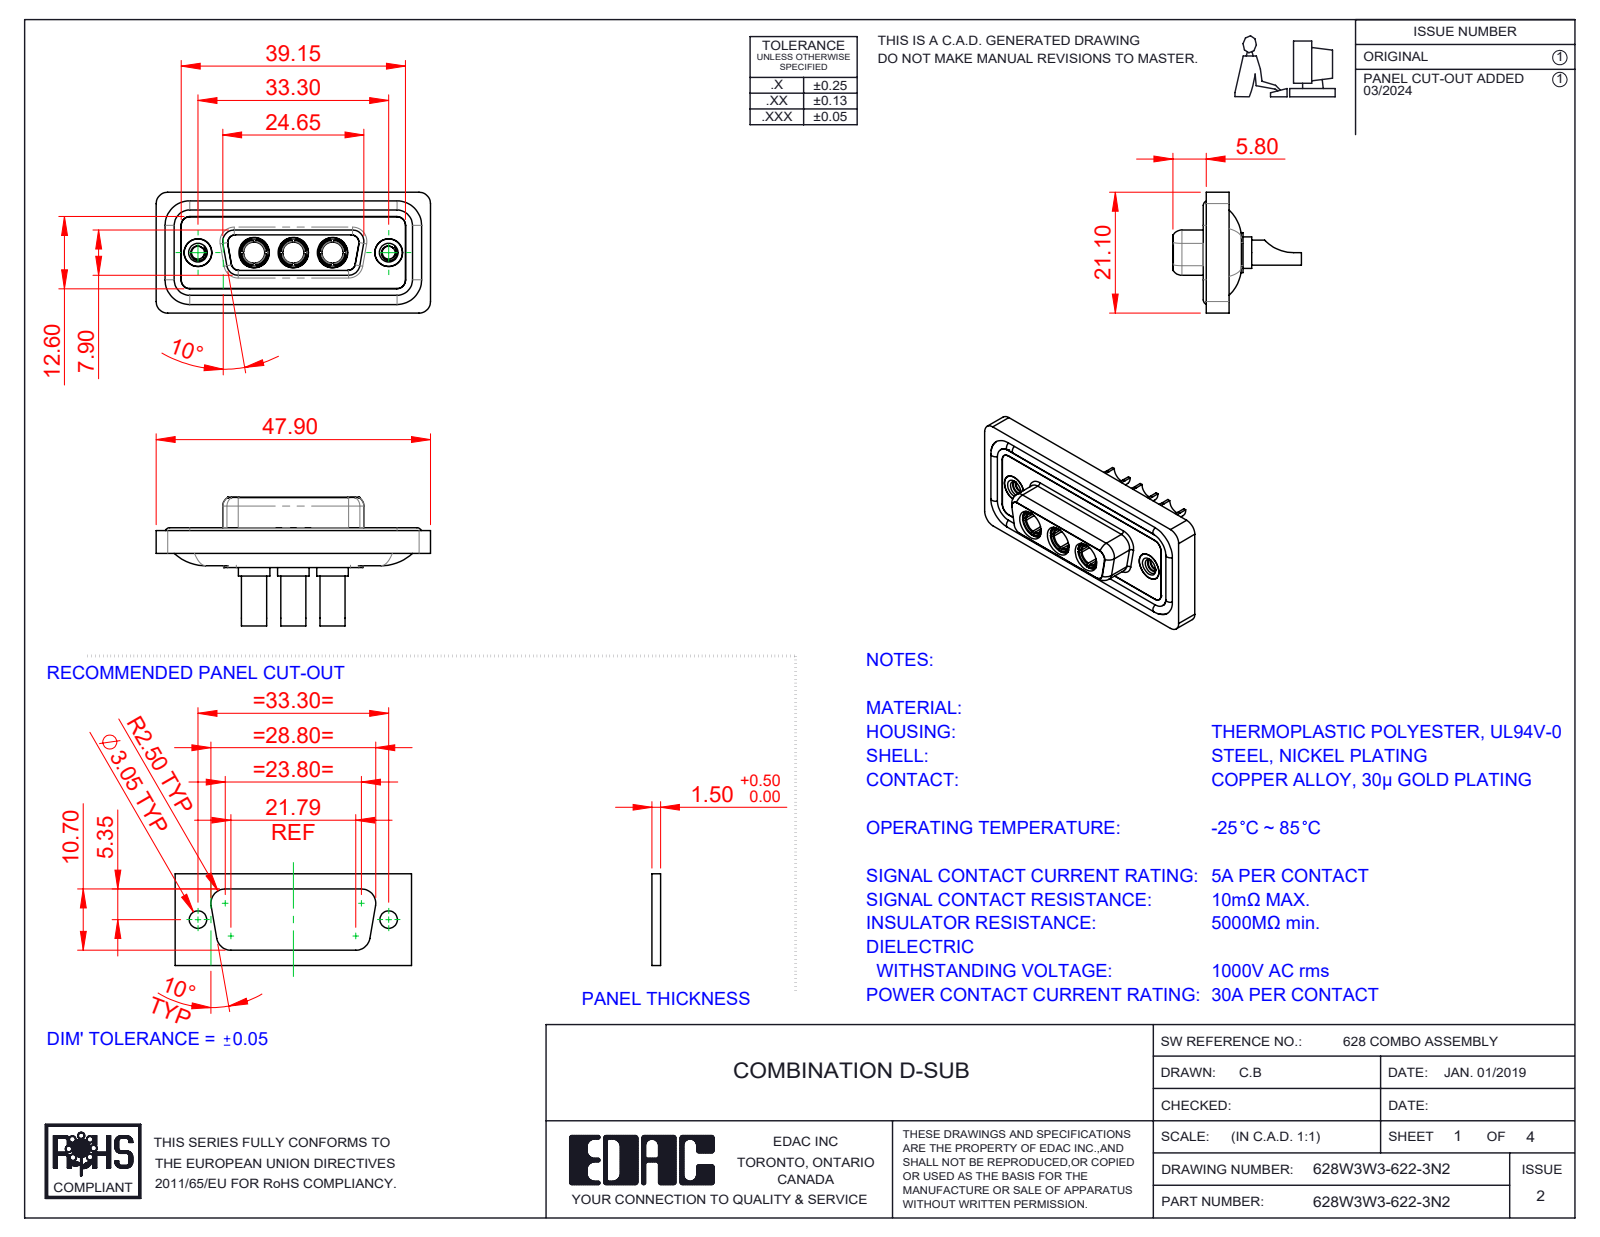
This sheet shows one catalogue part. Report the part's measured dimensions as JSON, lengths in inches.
{"part_name": "628Combo Shell Rear_15 Contacts; 628Combo Threaded Rivet_2; 628Combo Housing_3W3; 628Combo Shell Front_15 Contacts (+3 more)", "step_written_by": "SolidWorks 2023 (CONFIG_CONTROL_DESIGN)", "units": "inches", "bodies": {"solids": 13, "faces": 626, "planar": 201, "cylindrical": 266, "other": 159}, "overall_size": [1.886, 0.884, 0.831], "volume_in3": 0.372, "surface_area_in2": 15.59, "round_holes": [[0.191, 5], [0.138, 3], [0.146, 3], [0.209, 3], [0.089, 2], [0.157, 2], [0.159, 2], [0.197, 2]], "round_bosses_or_shafts": [[0.063, 4], [0.217, 3], [0.205, 3], [0.195, 3], [0.187, 3], [0.173, 3], [0.148, 3], [0.195, 2]], "partial_cylinders_radius": [[0.059, 22], [0.079, 20], [0.053, 12], [0.063, 8], [0.01, 4], [0.02, 4], [0.024, 4], [0.026, 4]], "face_to_face_distances": [0.016, 0.071, 0.063, 0.02, 0.293, 0.043, 0.114, 0.222, 0.278, 0.26], "hole_center_spacings": [0.27, 0.386, 0.656, 0.925, 0.539, 1.311]}
